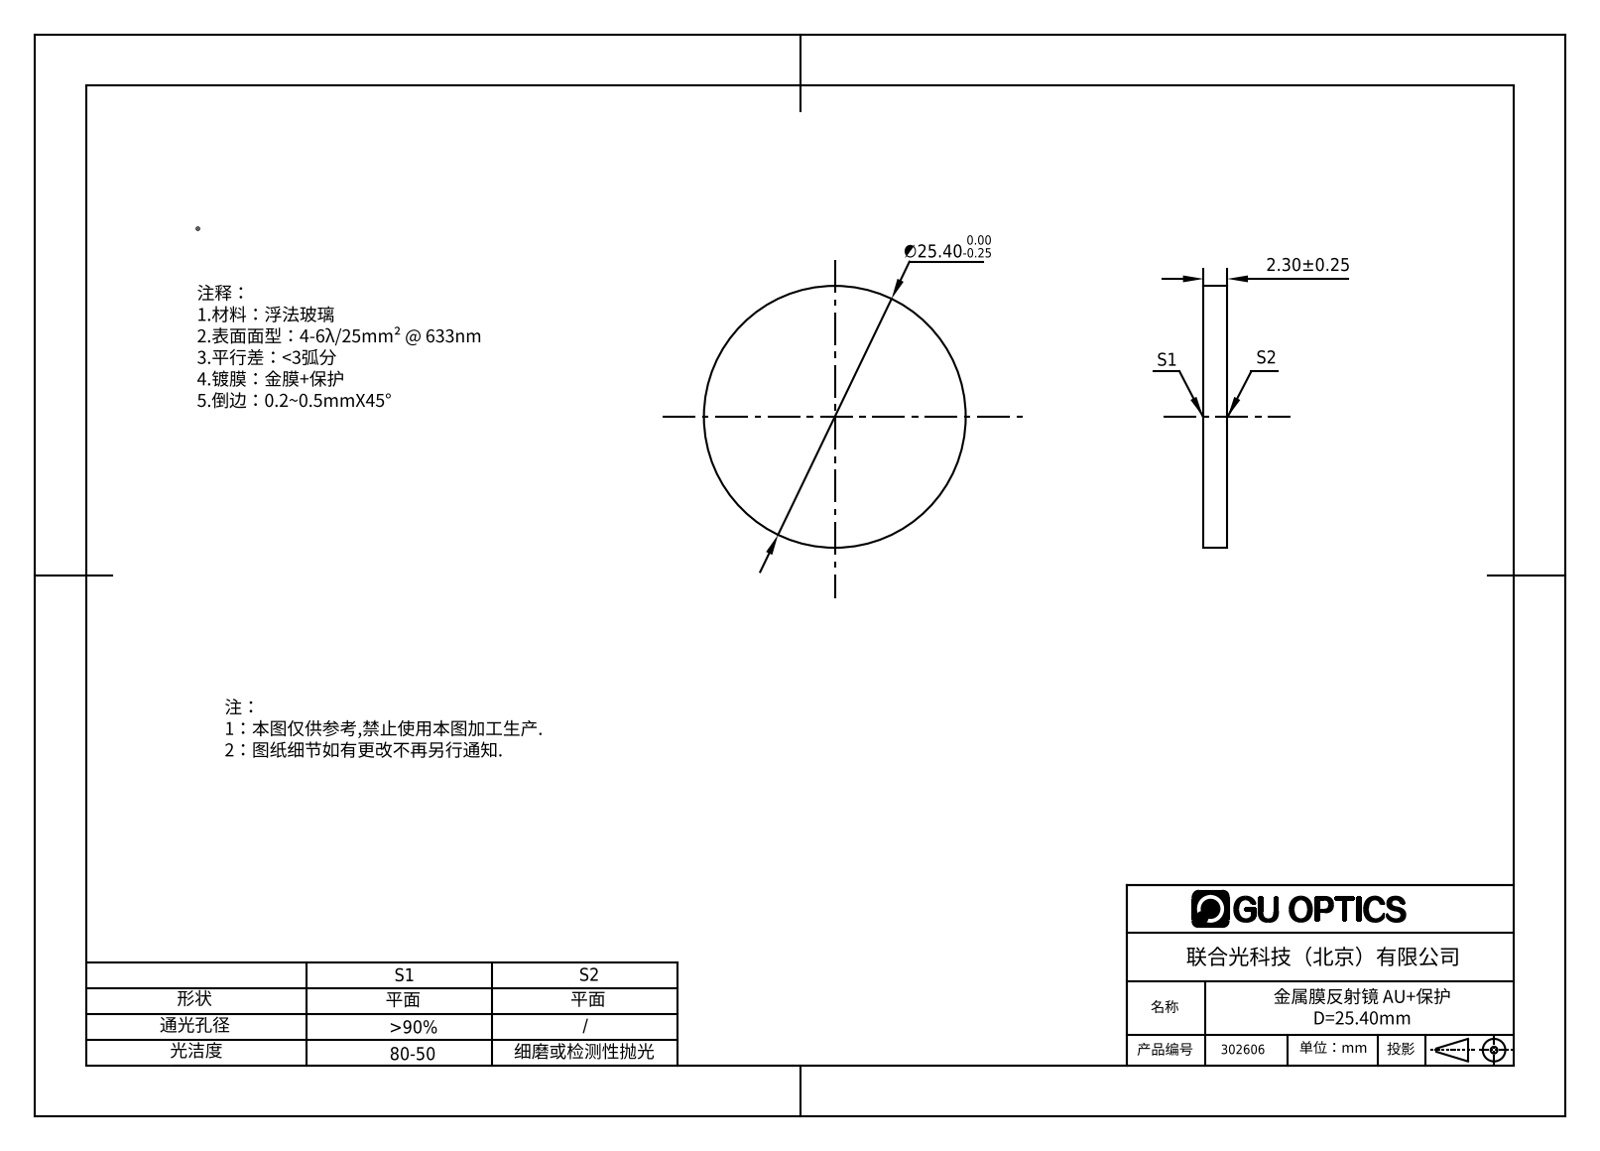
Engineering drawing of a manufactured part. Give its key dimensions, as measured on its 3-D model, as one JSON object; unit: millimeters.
{"part_name": "302519", "step_written_by": "SolidWorks 2016 (AUTOMOTIVE_DESIGN)", "units": "millimeters", "bodies": {"solids": 1, "faces": 4, "planar": 2, "cylindrical": 2, "other": 0}, "overall_size": [25.4, 25.4, 2.3], "volume_mm3": 1165, "surface_area_mm2": 1197, "round_bosses_or_shafts": [[25.4, 1]], "face_to_face_distances": [2.3]}
